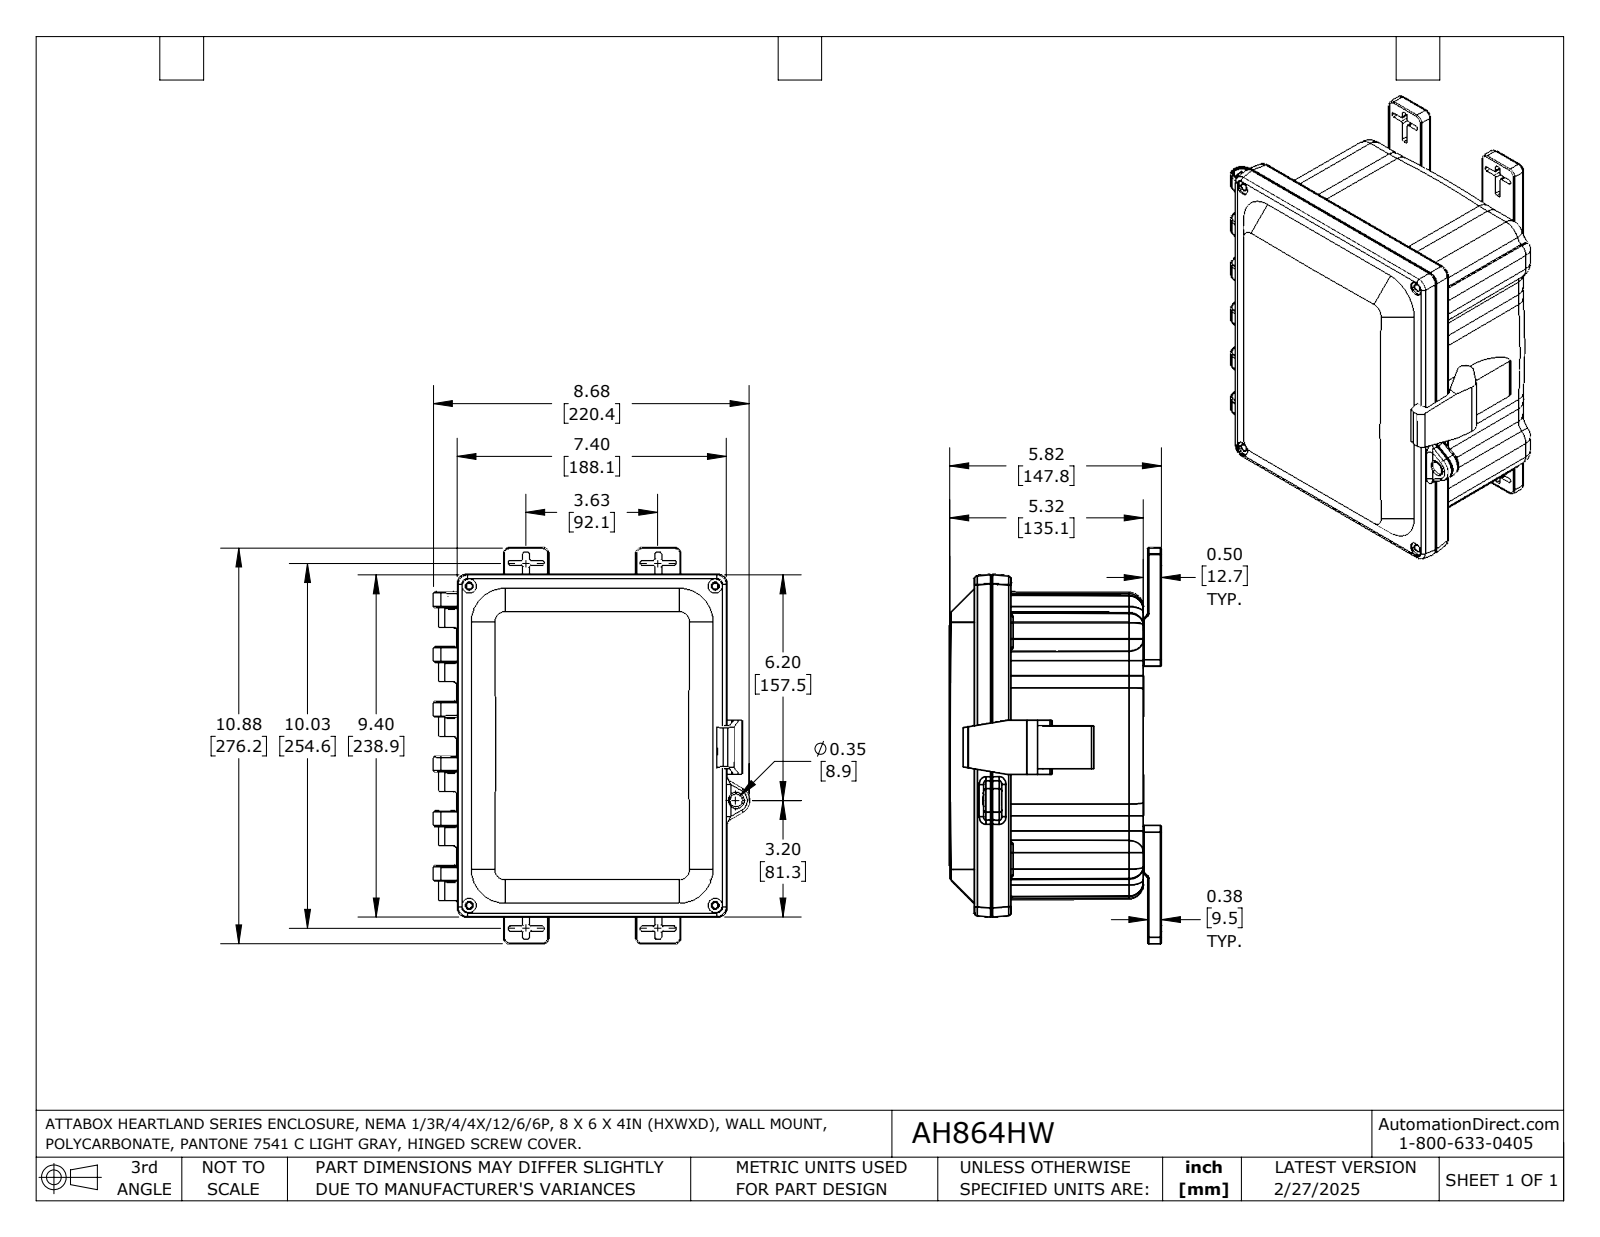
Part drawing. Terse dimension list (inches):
name: AH864HW
written by: SolidWorks 2024 (AUTOMOTIVE_DESIGN)
unit: in
bodies: 4 solids, 2156 faces (550 planar, 681 cylindrical, 925 other)
size: 10.875 × 8.676 × 5.82
volume: 58.11 in³; area: 665.1 in²
holes: 8× ⌀0.156, 4× ⌀0.195, 4× ⌀0.25, 4× ⌀0.313, 4× ⌀0.39, 1× ⌀0.327, 1× ⌀0.375, 1× ⌀0.45
bosses: 4× ⌀0.25, 1× ⌀0.313
rounds: 91× R0.065, 84× R0.05, 81× R0.035, 40× R0.03, 26× R0.02, 16× R0.18, 15× R0.01, 14× R0.025
face distances: 0.14, 4, 4.14, 0.5, 4.64, 0.133, 0.64, 4.5, 5.14, 0.125
hole spacings: 2.209, 5.418, 5.64, 6.75, 0.442, 1.767, 3.95, 5.946
